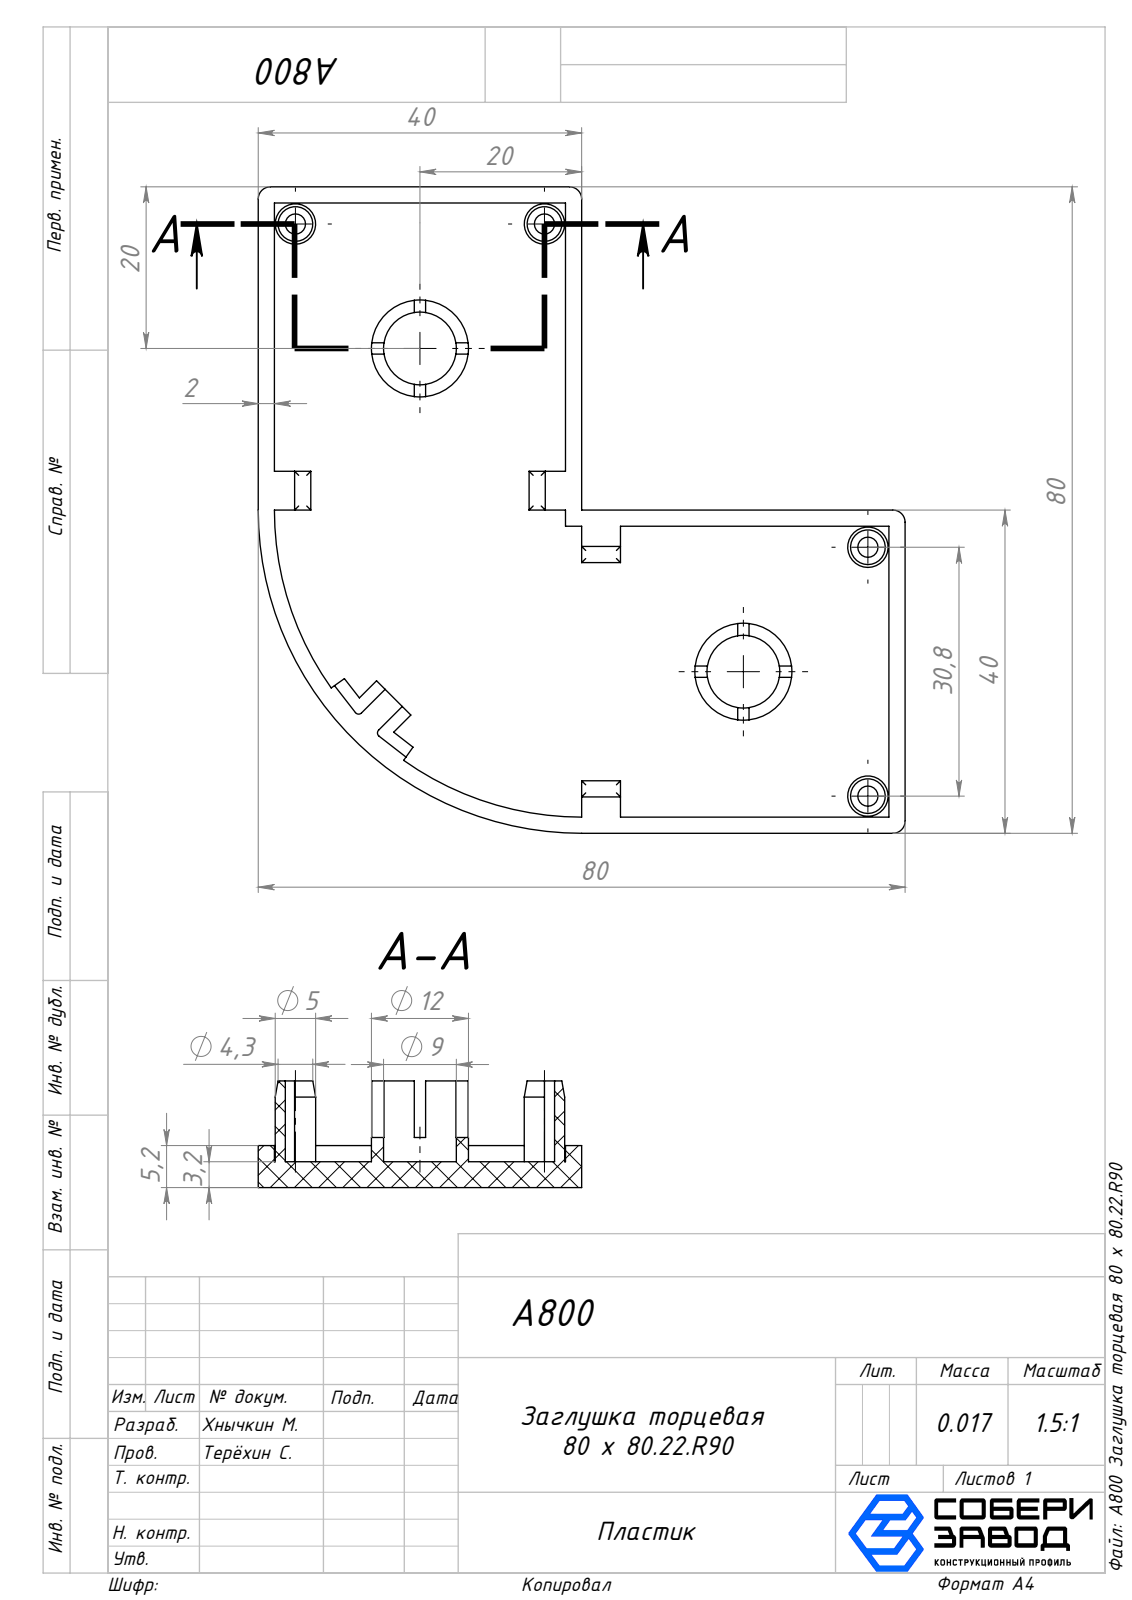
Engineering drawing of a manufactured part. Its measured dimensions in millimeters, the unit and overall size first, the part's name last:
Units: millimetres
Overall size (bounding box): 80 × 80 × 13.2
Round holes (diameter × count): ⌀2.5 ×4, ⌀9 ×2
Round bosses / shafts (diameter × count): ⌀5 ×4, ⌀12 ×2
Partial cylindrical surfaces — rounded edges, fillets, slot ends (radius × count): R0.5 ×14, R38 ×1, R40 ×1
Main face-to-face distances: 3.2, 2, 40, 5.2, 38, 80, 4.5, 33.5, 78, 6.5
Hole centre spacings: 21.78, 30.8, 56.57, 60.62, 78.35, 81.32, 100.13
Volume: 17 631 mm³ · Surface area: 14 115 mm²
Bodies: 1 solid, 145 faces (92 planar, 45 cylindrical, 8 other)
Part name (STEP PRODUCT): A800 Заглушка торцевая 80 х 80.22.R90
STEP written by: SolidWorks 2025 (AUTOMOTIVE_DESIGN)
